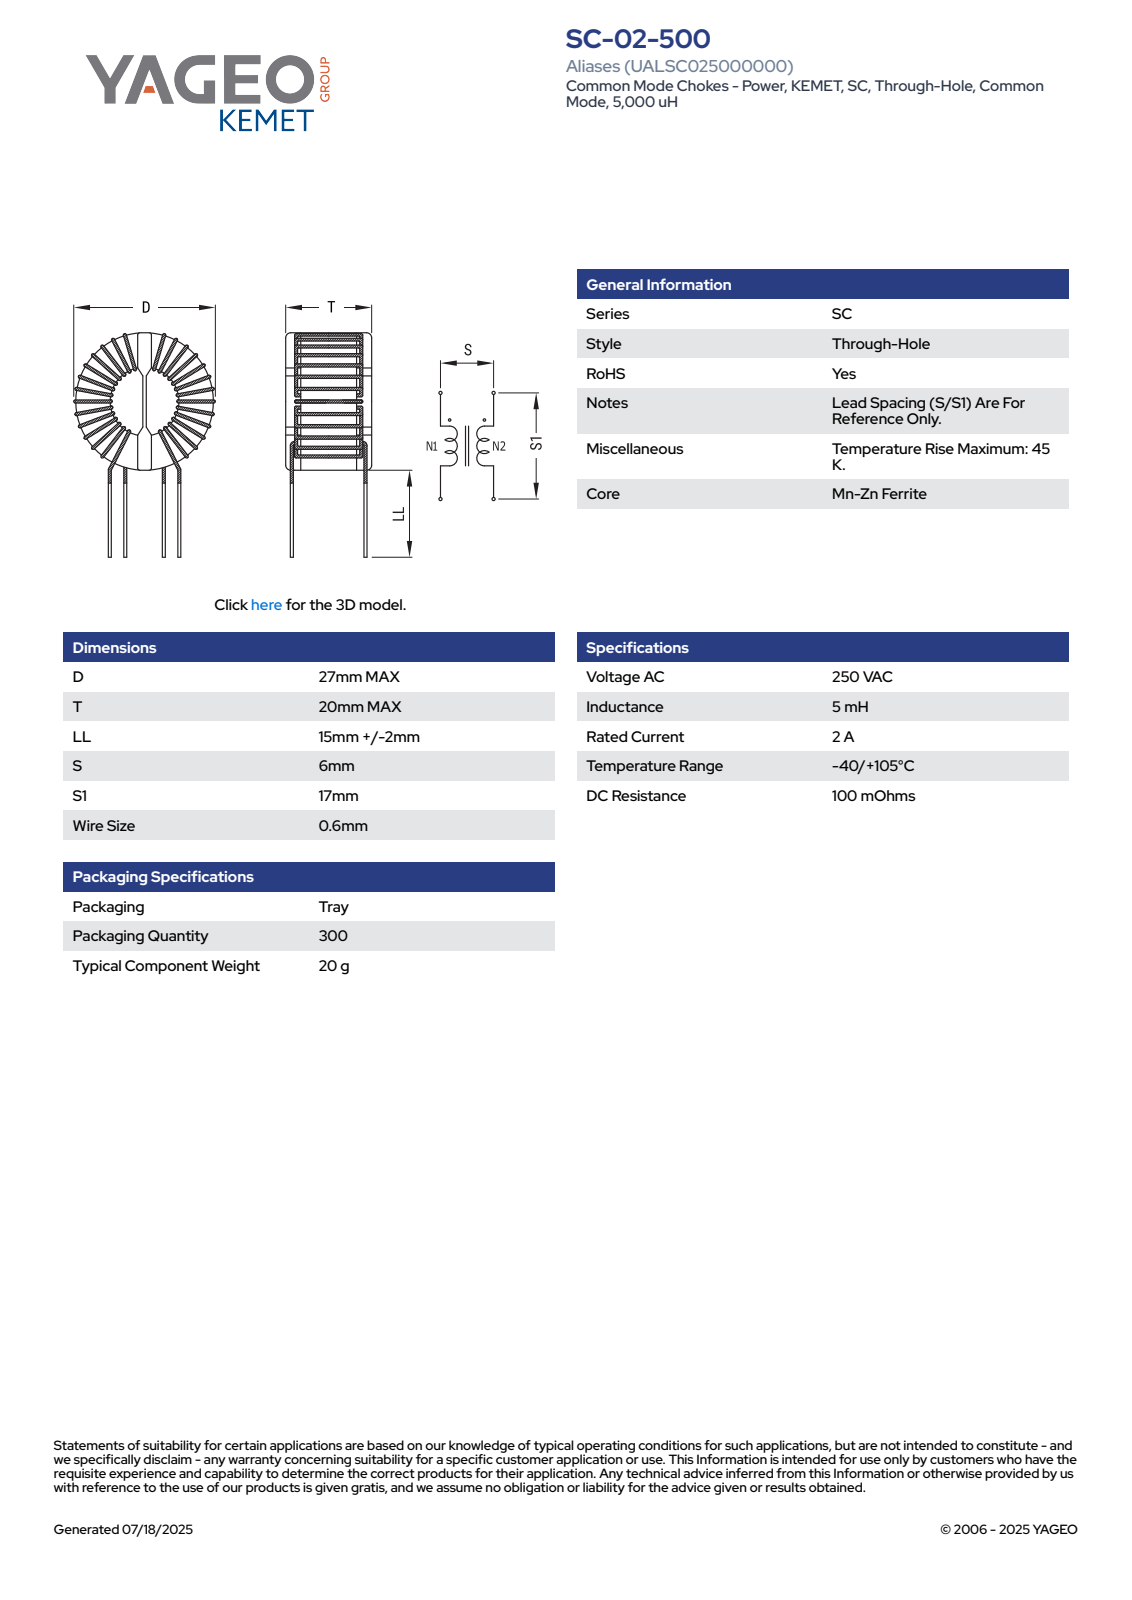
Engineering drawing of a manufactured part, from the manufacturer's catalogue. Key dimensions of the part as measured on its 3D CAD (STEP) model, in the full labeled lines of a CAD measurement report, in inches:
Part name (STEP PRODUCT): SC-02-500
STEP written by: SolidWorks 2018 (AUTOMOTIVE_DESIGN)
Units: inches
Bodies: 1 solid, 209 faces (62 planar, 79 cylindrical, 68 other)
Overall size (bounding box): 1.511 × 1.063 × 0.787
Volume: 0.467 in³ · Surface area: 6.535 in²
Round bosses / shafts (diameter × count): ⌀0.024 ×8
Partial cylindrical surfaces — rounded edges, fillets, slot ends (radius × count): R0.012 ×16, R0.008 ×4, R0.112 ×1, R0.163 ×1, R0.183 ×1, R0.187 ×1, R0.193 ×1, R0.364 ×1
Main face-to-face distances: 0.642, 0.047, 0.079, 0.126, 0.031, 0.073, 0.715, 0.137, 0.505, 0.154
